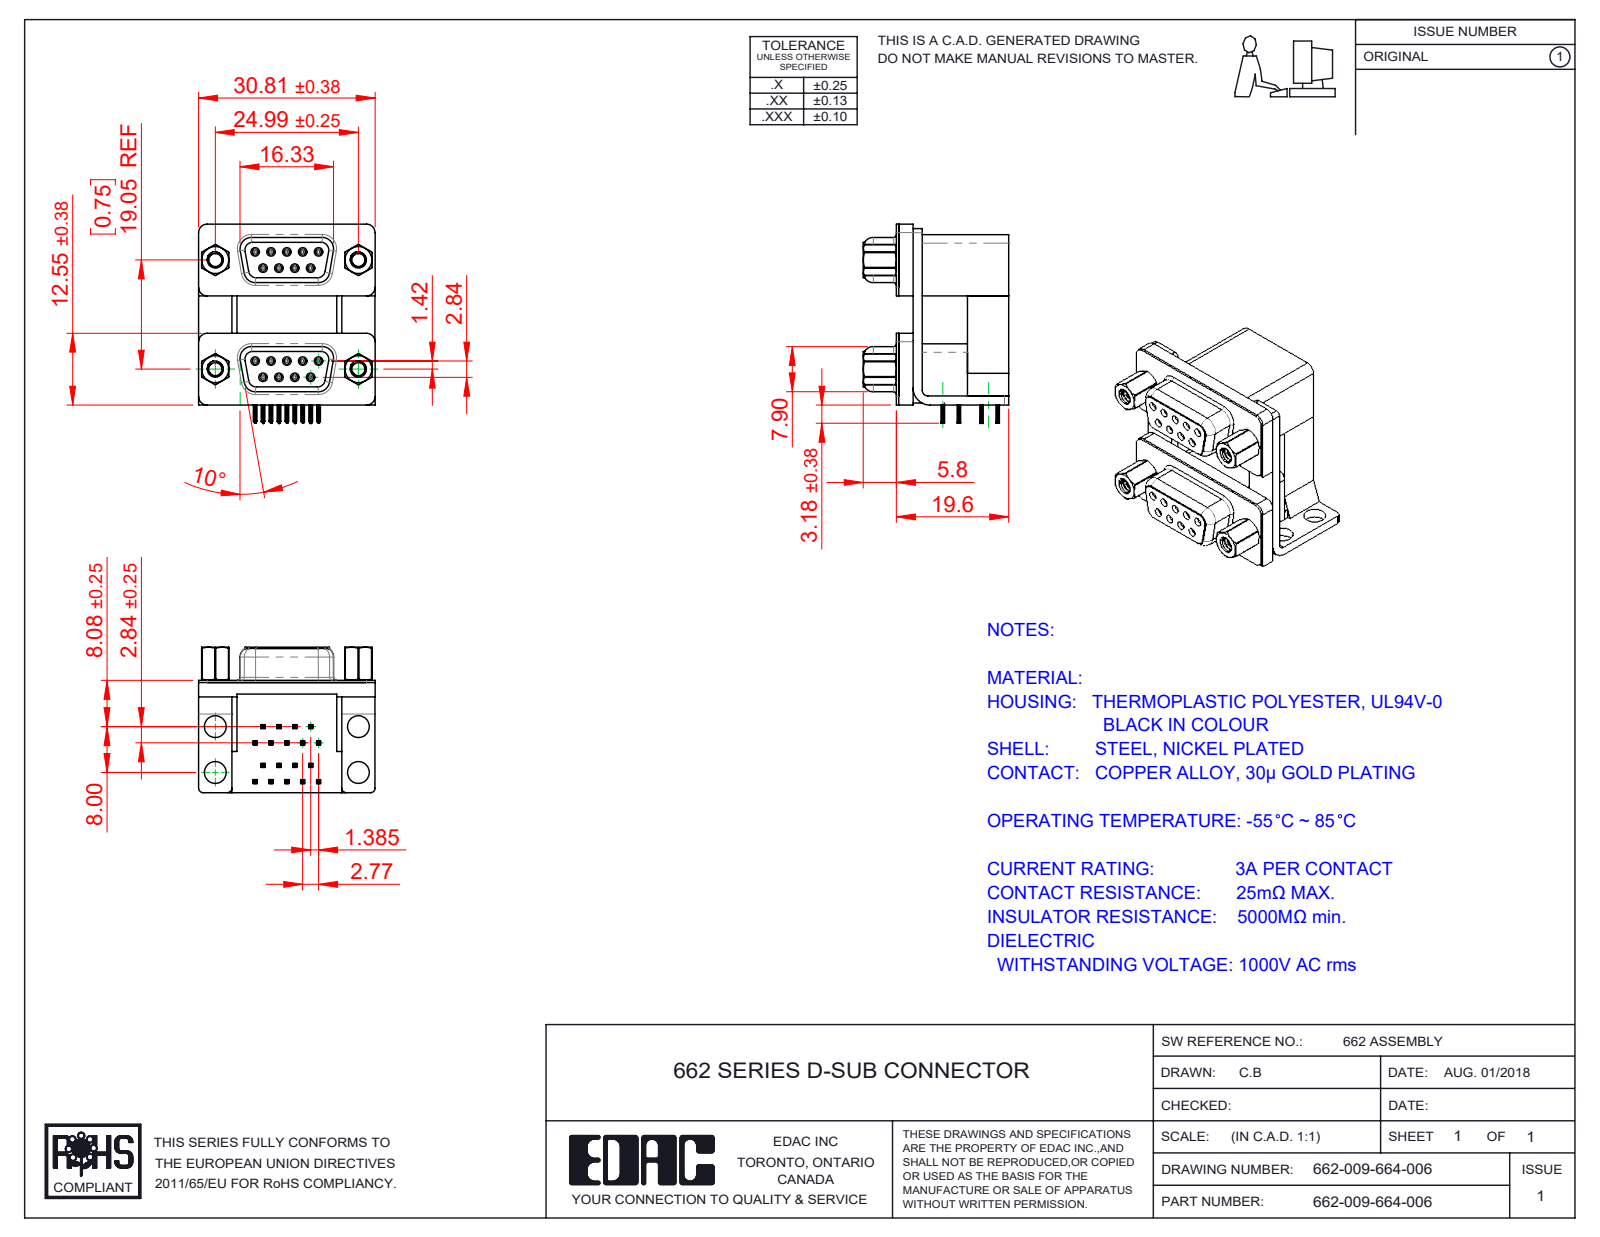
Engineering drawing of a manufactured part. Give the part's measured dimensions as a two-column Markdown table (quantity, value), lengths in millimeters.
| quantity | value |
| --- | --- |
| part name | 662 Contact Bottom Lower; 662 Mounting Bracket_NoneM; 662 4-40 Hex Standoff 5; 662 Threaded Rivet_4-40 (+8 more) |
| STEP written by | SolidWorks 2020 (CONFIG_CONTROL_DESIGN) |
| units | millimeters |
| bodies | 33 solids, 3362 faces (1418 planar, 940 cylindrical, 1004 other) |
| overall size | 34.78 × 30.81 × 25.4 |
| volume | 11 706 mm³ |
| surface area | 14 138 mm² |
| round holes (diameter × count) | 0.8 × 18, 0.9 × 18, 2.26 × 4, 2.29 × 4, 3.5 × 4, 3.8 × 4, 4 × 4, 4.8 × 4, 5 × 4 |
| round bosses / shafts (diameter × count) | 1.2 × 18, 4.9 × 4, 4.75 × 4, 3.9 × 4, 2.79 × 4 |
| partial cylindrical surfaces (radius × count) | 0.1 × 144, 0.15 × 72, 0.35 × 36, 0.34 × 18, 1.35 × 16, 1.5 × 12, 0.28 × 8, 0.5 × 8 |
| main face-to-face distances | 0.4, 2.5, 16.7, 19.2, 19.05, 2.9, 12, 12.4, 19.6, 7.2 |
| hole center spacings | 3.16, 19.25, 2.77, 19.05, 19.84, 21.93, 5.54, 22.28 |
